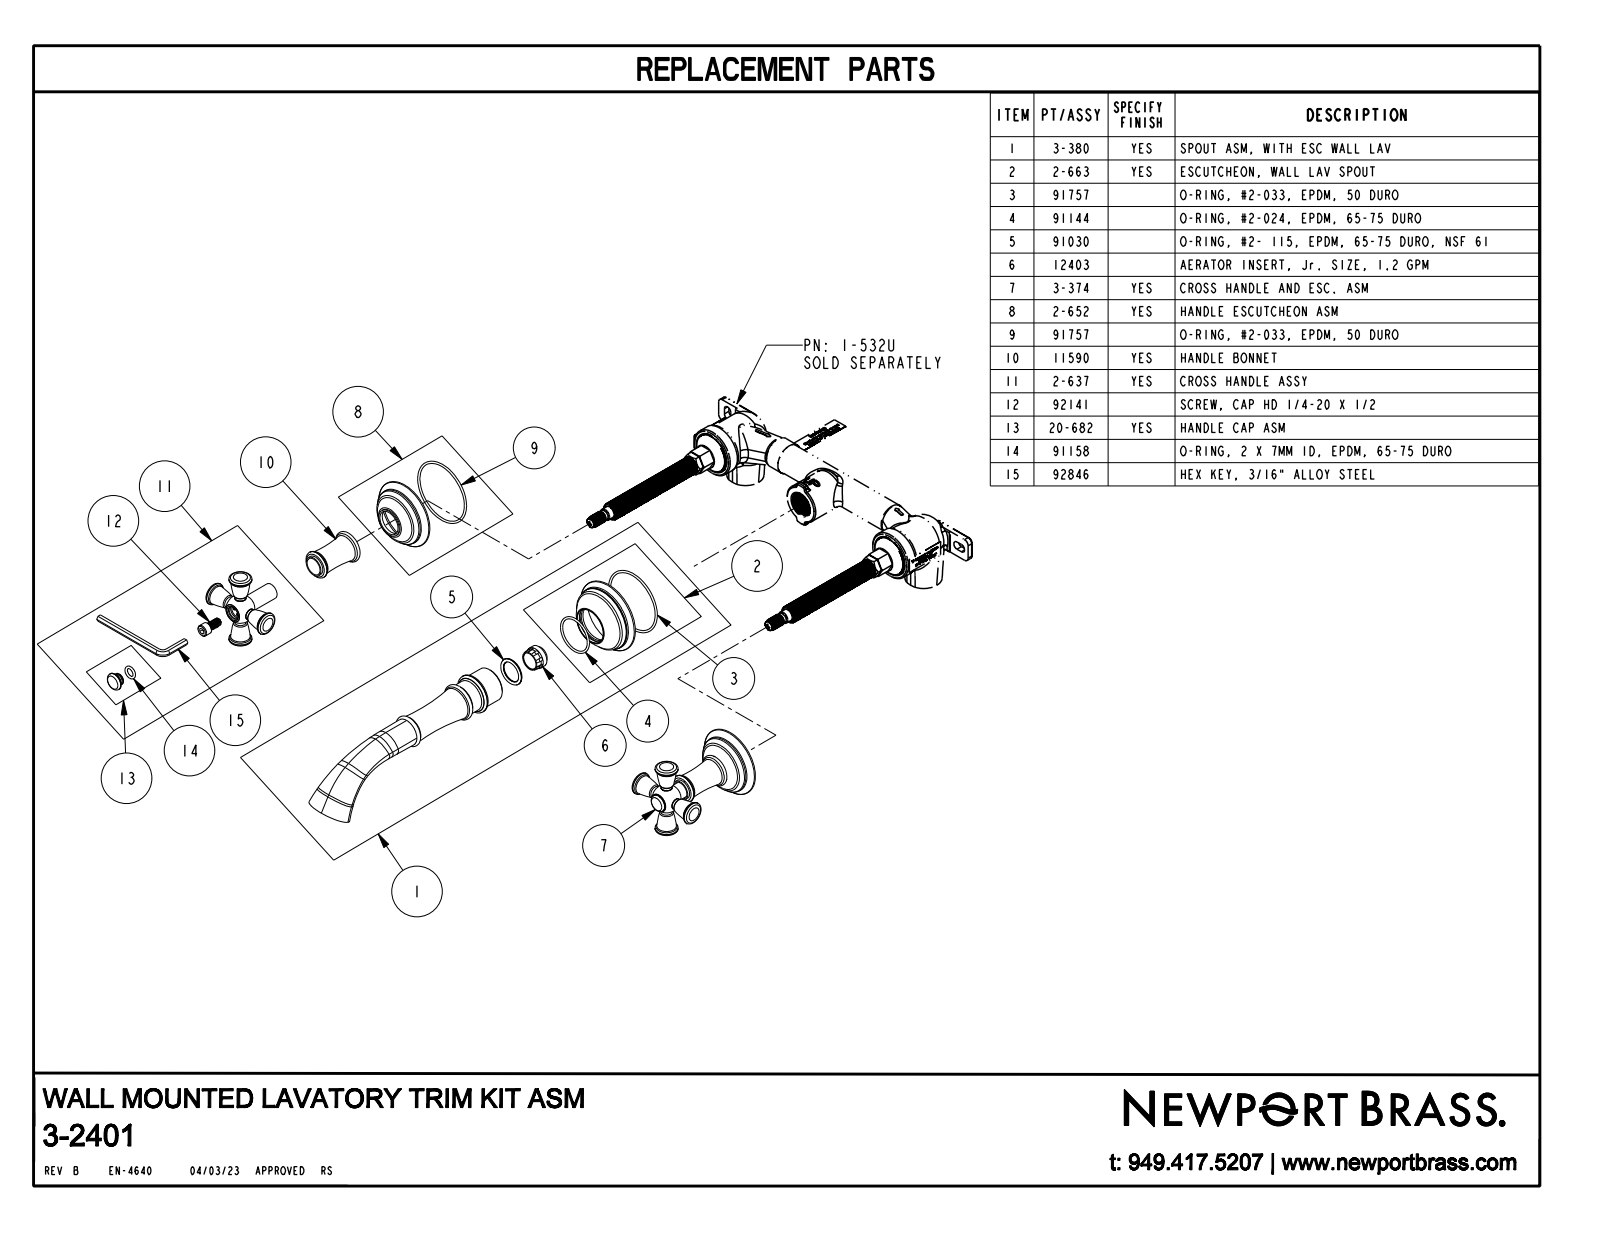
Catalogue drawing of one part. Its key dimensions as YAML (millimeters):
part_name: "3-2401_SW0002"
step_written_by: "CREO PARAMETRIC BY PTC INC, 2018400 (AUTOMOTIVE_DESIGN)"
units: millimeters
bodies: {solids: 3, faces: 348, planar: 26, cylindrical: 68, other: 254}
overall_size: [264.2, 192.9, 68.7]
volume: 197600
surface_area: 53550
round_holes:
  - {diameter: 20.3, count: 2}
  - {diameter: 48.5, count: 2}
  - {diameter: 53.8, count: 2}
round_bosses_or_shafts:
  - {diameter: 18.3, count: 3}
  - {diameter: 9.1, count: 3}
  - {diameter: 49.8, count: 2}
  - {diameter: 22.9, count: 2}
  - {diameter: 16.5, count: 2}
  - {diameter: 14.2, count: 2}
  - {diameter: 13.1, count: 2}
  - {diameter: 32.5, count: 1}
face_to_face_distances: [17, 1.3, 15.7, 15.4, 14.1, 1.6, 54.4, 53.1, 38.9, 37.3]
hole_center_spacings: [200]
